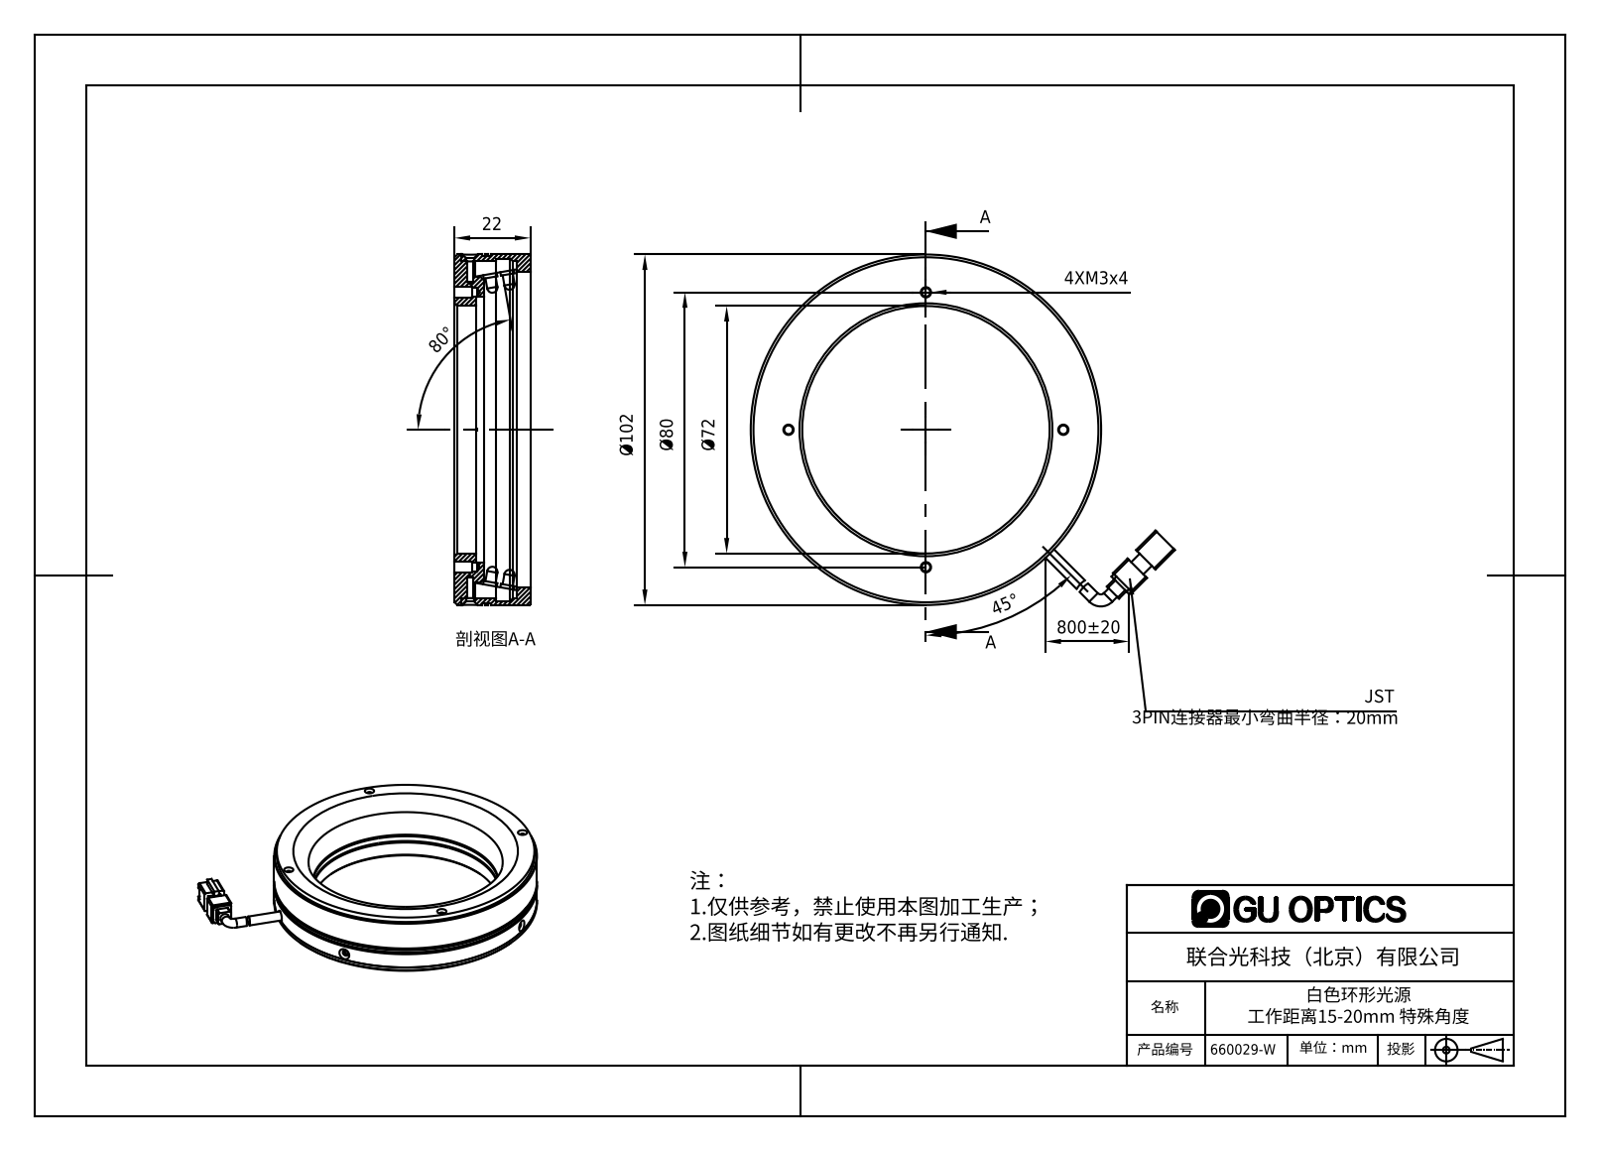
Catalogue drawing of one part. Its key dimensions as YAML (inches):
part_name: "660029-W"
step_written_by: "SolidWorks 2016 (AUTOMOTIVE_DESIGN)"
units: inches
bodies: {solids: 111, faces: 2068, planar: 1343, cylindrical: 545, other: 180}
overall_size: [4.861, 4.032, 0.957]
volume: 3.63
surface_area: 93.35
round_holes:
  - {diameter: 0.049, count: 4}
  - {diameter: 0.067, count: 4}
  - {diameter: 0.098, count: 4}
  - {diameter: 0.118, count: 4}
  - {diameter: 0.063, count: 2}
  - {diameter: 0.094, count: 2}
  - {diameter: 0.138, count: 2}
  - {diameter: 2.835, count: 1}
  - {diameter: 3.055, count: 1}
  - {diameter: 3.622, count: 1}
  - {diameter: 3.858, count: 1}
  - {diameter: 3.921, count: 1}
round_bosses_or_shafts:
  - {diameter: 0.15, count: 105}
  - {diameter: 0.118, count: 105}
  - {diameter: 0.138, count: 2}
  - {diameter: 4.016, count: 1}
  - {diameter: 3.976, count: 1}
  - {diameter: 3.937, count: 1}
  - {diameter: 3.508, count: 1}
  - {diameter: 2.992, count: 1}
partial_cylinders:
  - {radius: 0.02, count: 8}
  - {radius: 0.039, count: 4}
  - {radius: 0.063, count: 1}
  - {radius: 0.276, count: 1}
face_to_face_distances: [0.866, 0.079, 0.236, 0.157, 0.63, 0.709, 0.945, 0.098, 0.472, 0.039]
hole_center_spacings: [1.346, 3.185, 1.575, 1.87, 2.227, 2.645, 3.15, 3.741]
